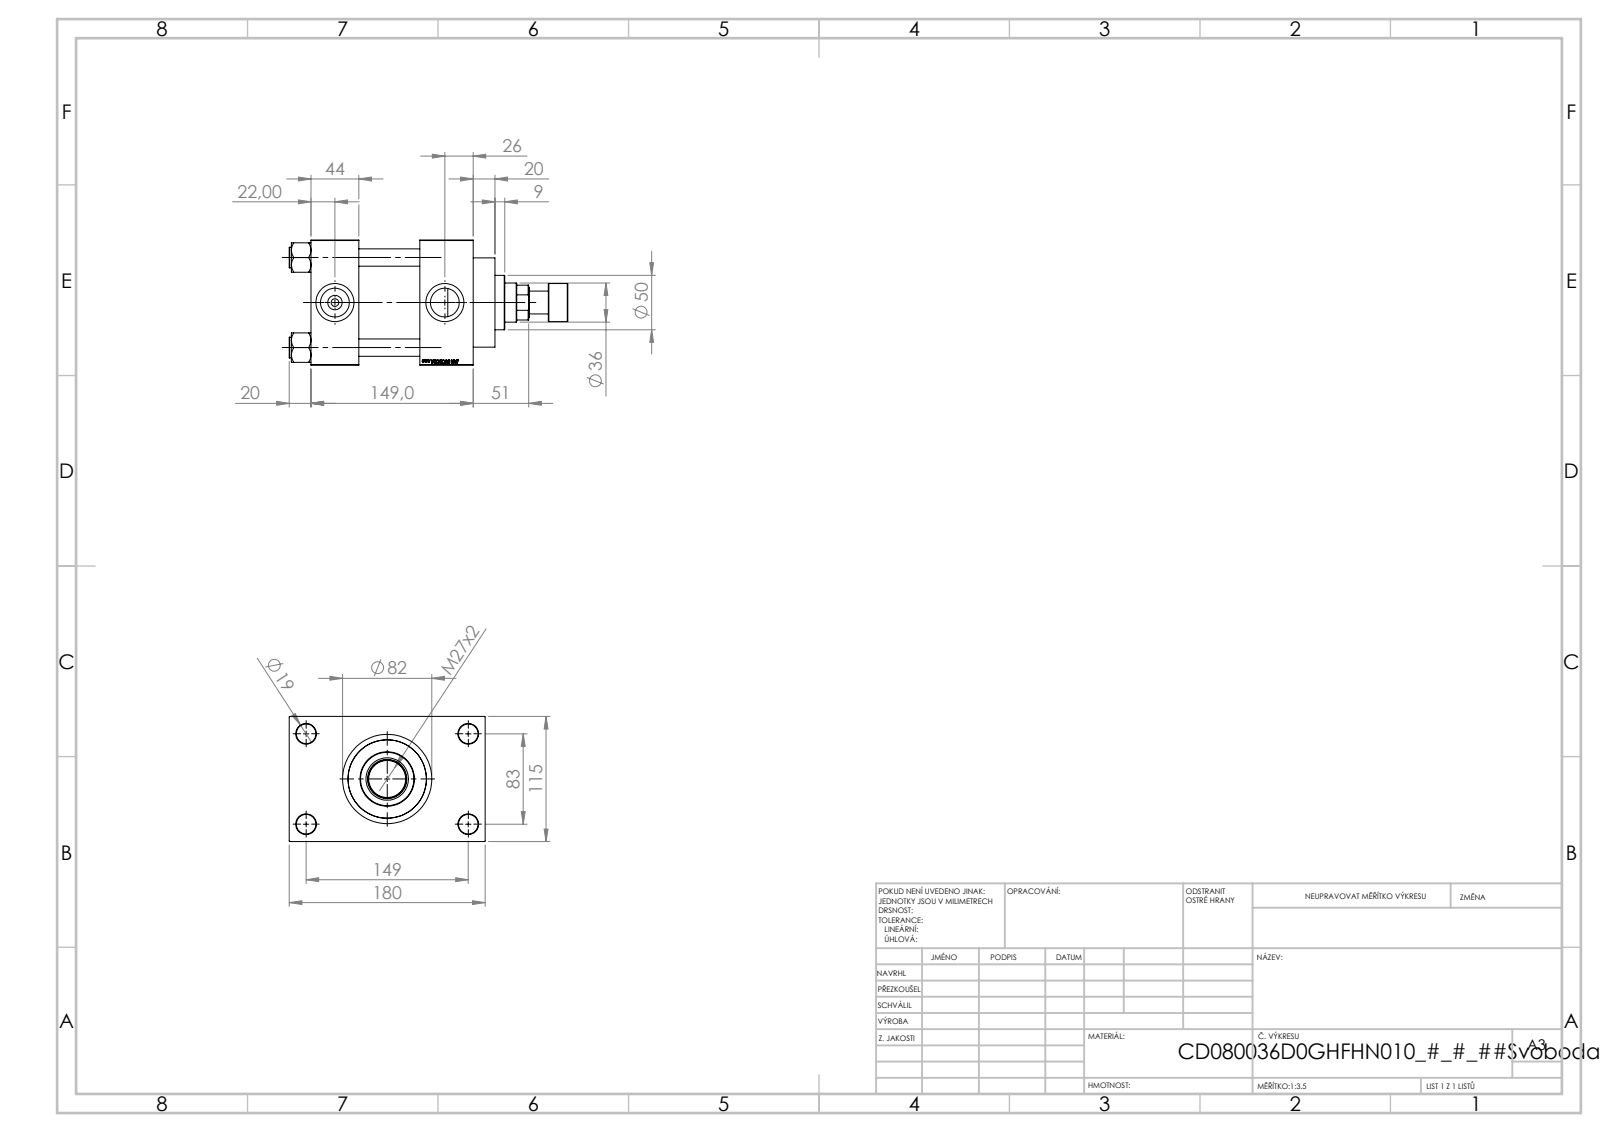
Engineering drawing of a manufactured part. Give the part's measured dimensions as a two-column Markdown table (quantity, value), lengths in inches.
| quantity | value |
| --- | --- |
| part name | V215CD_D_Body; V215CR_ROD_END_F; V215CD_VC_A; V215CD_VCP_D (+2 more) |
| STEP written by | SolidWorks 2019 (CONFIG_CONTROL_DESIGN) |
| units | inches |
| bodies | 12 solids, 1165 faces (549 planar, 92 cylindrical, 524 other) |
| overall size | 10.079 × 7.087 × 4.528 |
| volume | 120.6 in³ |
| surface area | 455.4 in² |
| round holes (diameter × count) | 0.63 × 4, 0.709 × 4, 0.276 × 2, 1.041 × 2, 1.378 × 2, 1.004 × 1, 1.417 × 1, 1.535 × 1, 2.402 × 1, 2.835 × 1, 3.15 × 1 |
| round bosses / shafts (diameter × count) | 0.748 × 4, 3.386 × 1, 3.228 × 1, 1.969 × 1, 1.378 × 1, 0.827 × 1 |
| main face-to-face distances | 4.528, 2.205, 4.134, 1.929, 3.937, 1.732, 5.866, 1.28, 5.807, 2.717 |
| hole center spacings | 1.305, 2.302, 3.256, 3.357, 3.513, 4.561, 5.607, 3.268 |
